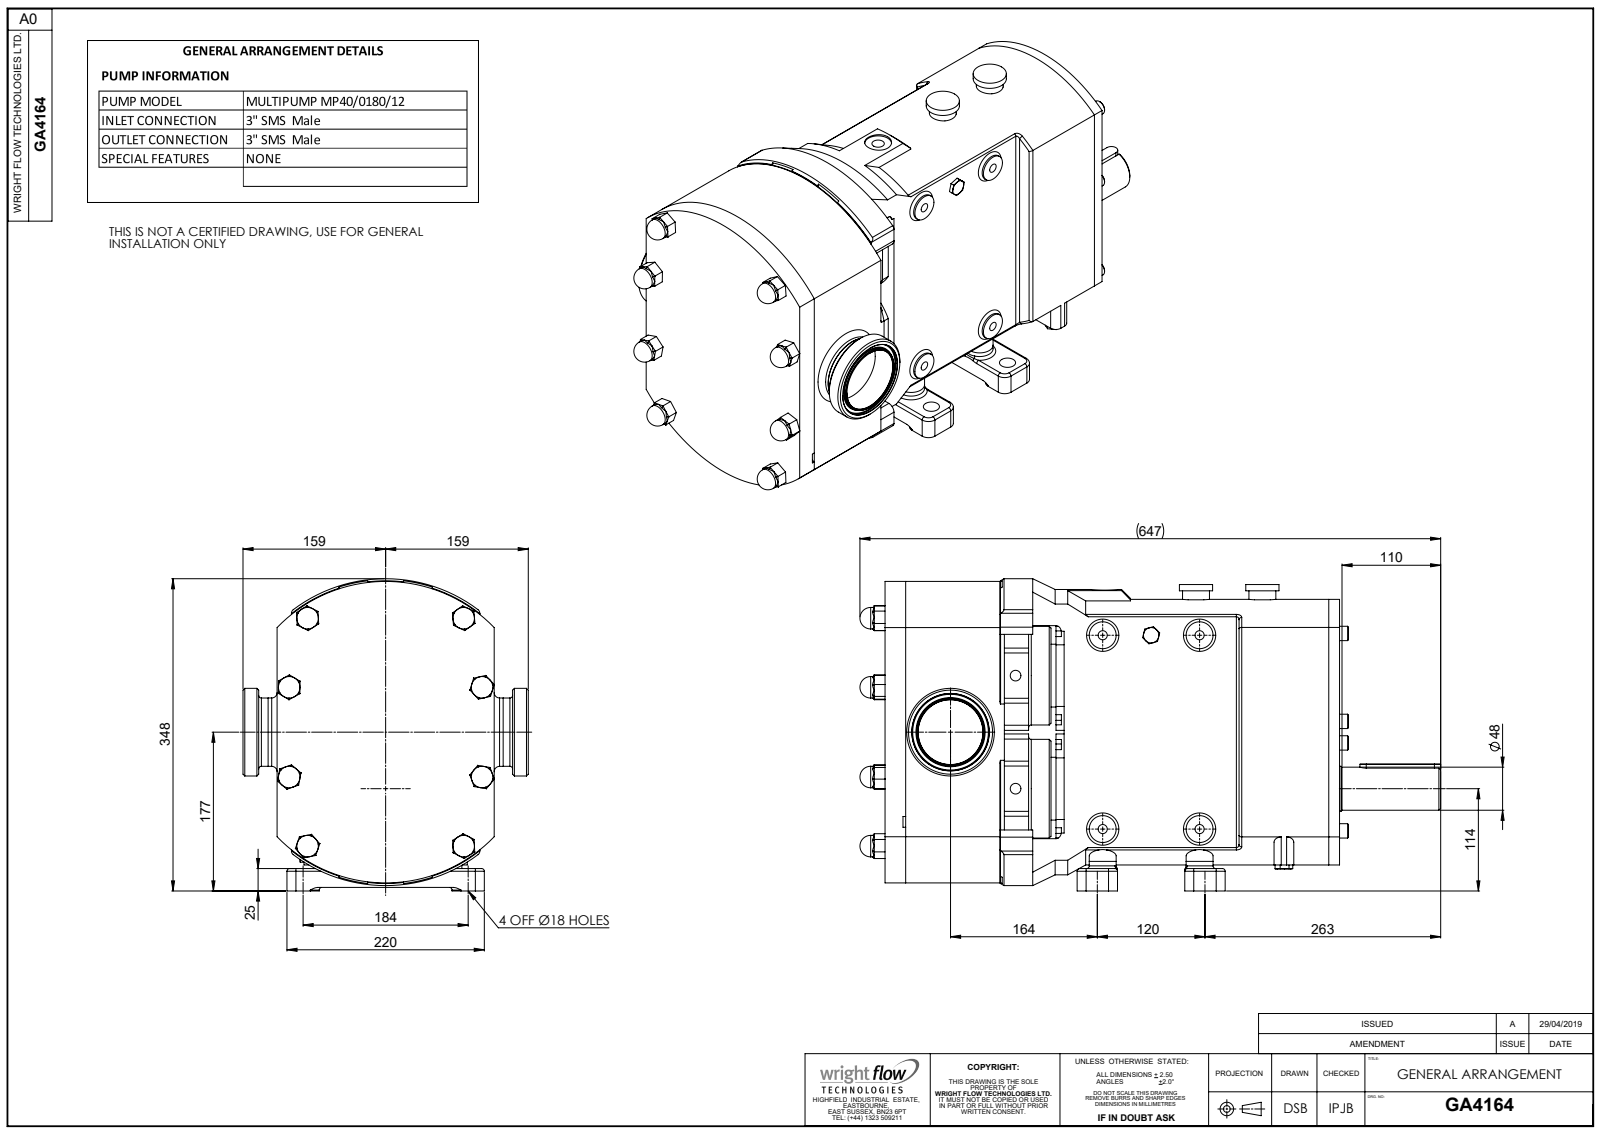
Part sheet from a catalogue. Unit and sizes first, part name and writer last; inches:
Units: inches
Overall size (bounding box): 25.487 × 13.701 × 12.52
Round holes (diameter × count): ⌀0.402 ×4, ⌀0.709 ×4, ⌀0.468 ×2, ⌀1.378 ×2, ⌀0.544 ×1, ⌀1.181 ×1, ⌀2.843 ×1, ⌀3.386 ×1
Round bosses / shafts (diameter × count): ⌀1.181 ×10, ⌀0.945 ×8, ⌀0.63 ×6, ⌀4.331 ×2, ⌀2.756 ×2, ⌀1.457 ×2, ⌀1.25 ×2, ⌀9.843 ×1
Partial cylindrical surfaces — rounded edges, fillets, slot ends (radius × count): R0.394 ×24, R0.118 ×22, R0.315 ×20, R0.236 ×10, R0.197 ×4, R0.433 ×4, R0.276 ×2, R0.512 ×2
Main face-to-face distances: 0.827, 1.181, 6.339, 2.008, 7.52, 8.346, 5.512, 19.946, 7.165, 9.528
Hole centre spacings: 3.636, 3.643, 3.781, 4.214, 4.252, 4.412, 4.724, 5.646
Volume: 1 608 in³ · Surface area: 1 410 in²
Bodies: 3 solids, 977 faces (369 planar, 279 cylindrical, 329 other)
Part name (STEP PRODUCT): GA4164; Copy of CP40S-0180 H BSD^GA4164; Copy of Z94-5101-55 - 3 INCH SMS681^GA4164
STEP written by: SolidWorks 2023 (AUTOMOTIVE_DESIGN)
